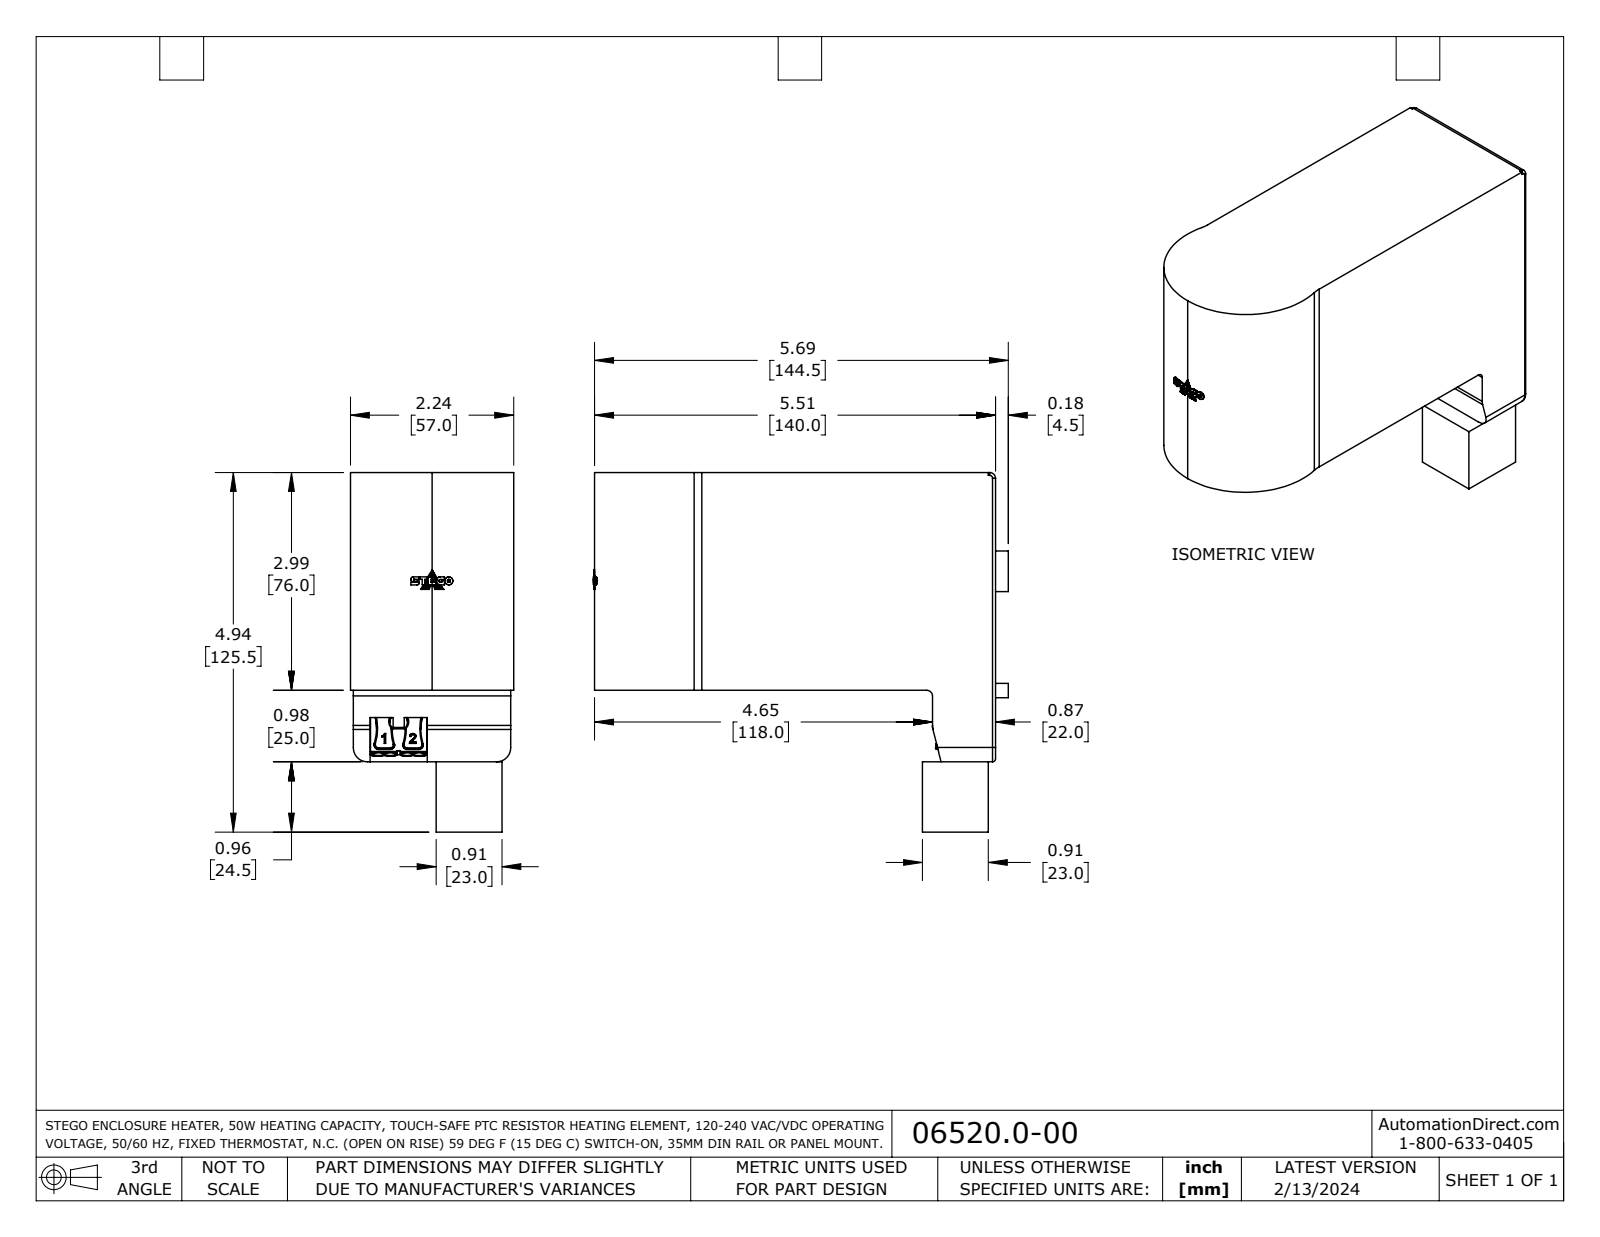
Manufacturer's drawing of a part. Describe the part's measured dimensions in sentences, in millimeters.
The part is named "STEP_LTF065_1". Its 3-D file was written by "SolidWorks 2022 (AUTOMOTIVE_DESIGN)". It is 1 solid with 473 faces: 234 planar, 125 cylindrical and 114 other. Overall it measures 144.9 by 125.5 by 57 millimeters. Its volume is 138 668 cubic millimeters and its surface area 91 038 square millimeters. Partial cylindrical surfaces (rounded edges, fillets, slot ends): 11 of radius 0.4, 6 of radius 0.3, 6 of radius 2, 5 of radius 1, 4 of radius 0.7, 4 of radius 1.5, 4 of radius 18.75, 2 of radius 2.5. The main face-to-face distances are 2.5, 52.5, 73.5, 55, 50, 76, 71, 5, 3.5, 17.
